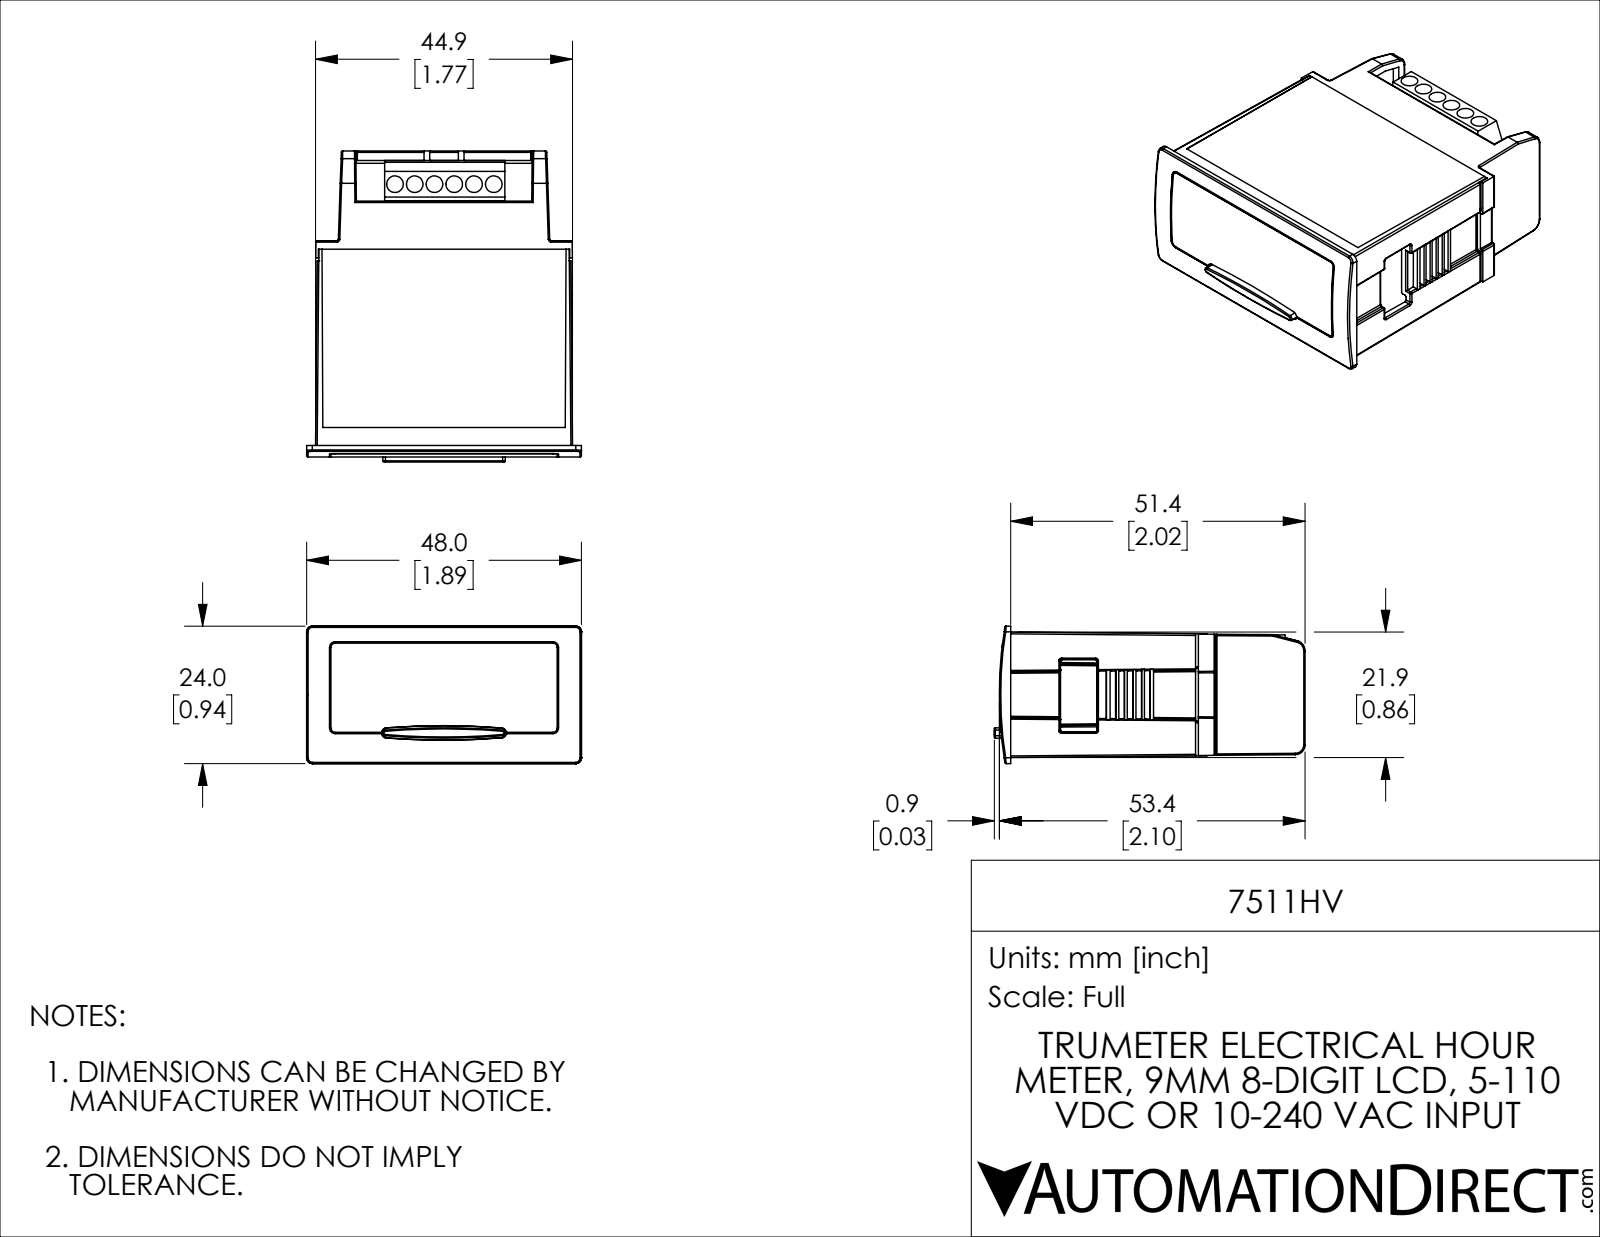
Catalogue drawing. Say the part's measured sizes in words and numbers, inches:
The part is named "7511HV". Its 3-D file was written by "SolidWorks 2021 (CONFIG_CONTROL_DESIGN)". It is 2 solids with 1771 faces: 1106 planar, 291 cylindrical and 374 other. Overall it measures 2.137 by 1.89 by 0.945 inches. Its volume is 0.944 cubic inches and its surface area 33.63 square inches. Round holes: 6 of diameter 0.114. Round bosses or shafts: 3 of diameter 0.15, 1 of diameter 0.069. Partial cylindrical surfaces (rounded edges, fillets, slot ends): 157 of radius 0.01, 12 of radius 0.039, 11 of radius 0.02, 4 of radius 0.012, 4 of radius 0.03, 2 of radius 0.019, 2 of radius 0.069, 2 of radius 5.065. The main face-to-face distances are 0.804, 0.067, 0.069, 1.668, 0.735, 0.802, 0.051, 0.059, 0.043, 1.711. The hole center spacings are 0.136, 0.272, 0.407, 0.543, 0.679.
